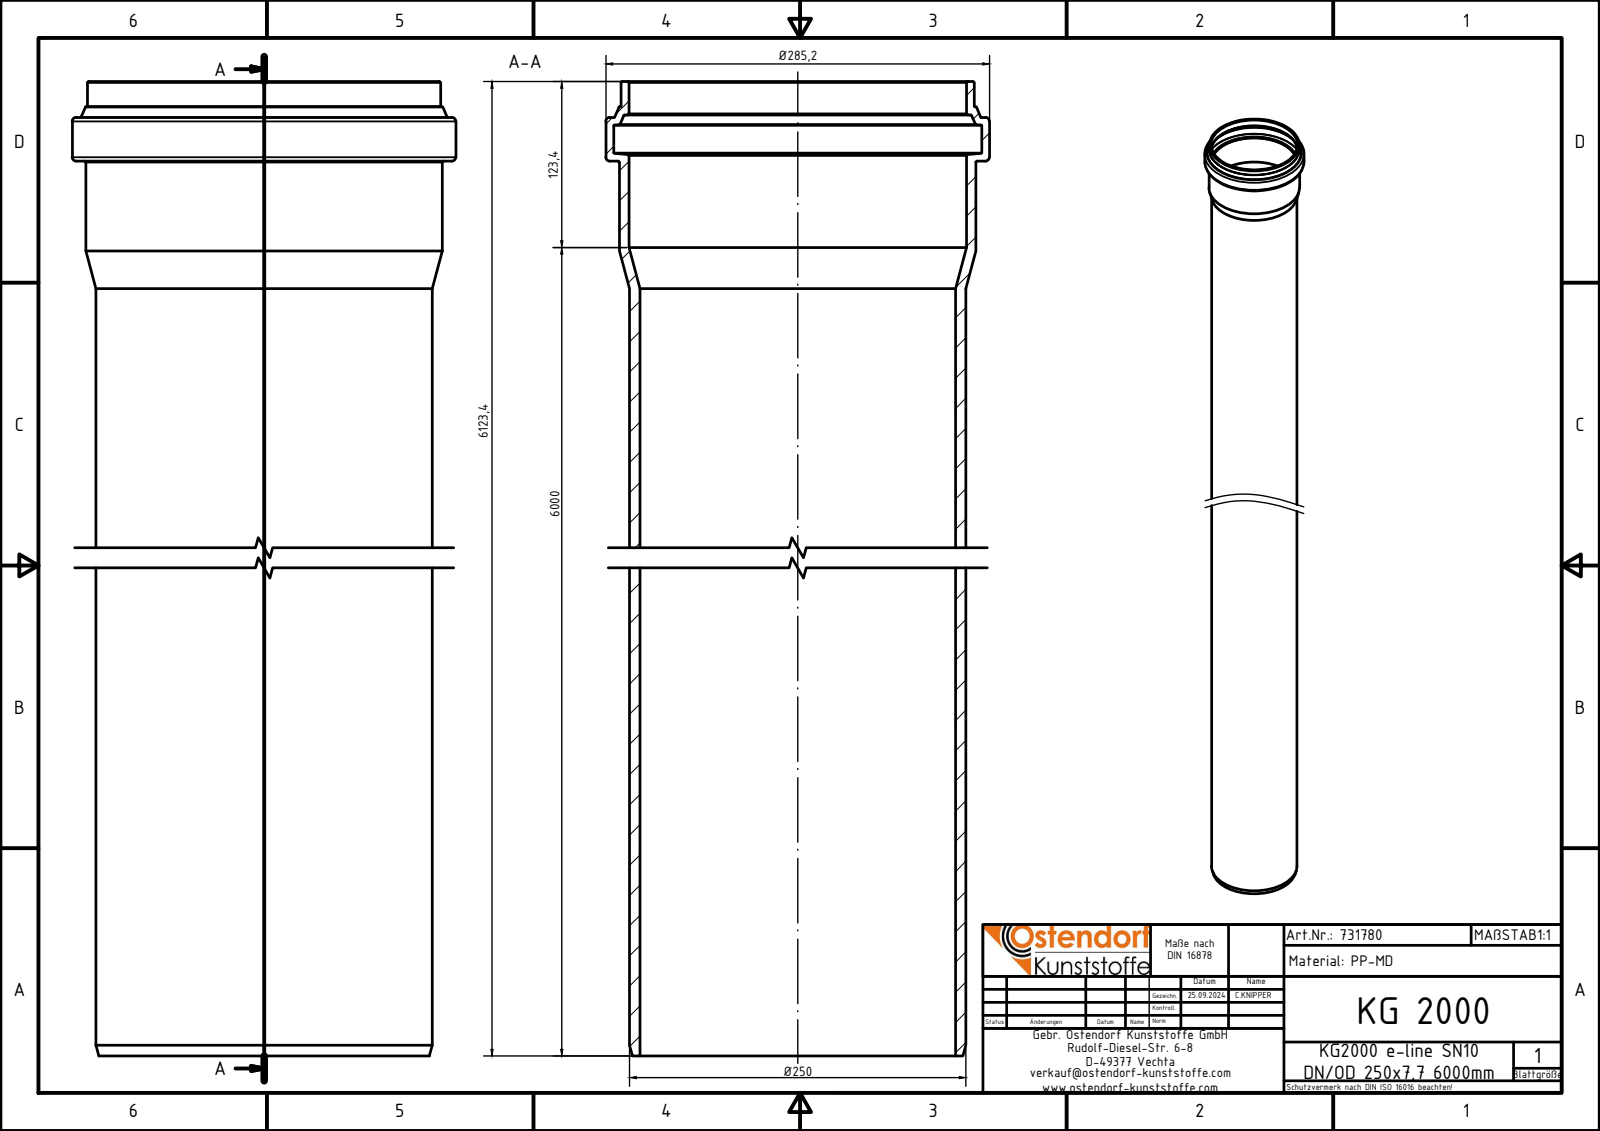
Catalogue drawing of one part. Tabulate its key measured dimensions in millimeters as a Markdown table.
| quantity | value |
| --- | --- |
| part name | 731780z |
| STEP written by | Autodesk Inventor 2024 (AUTOMOTIVE_DESIGN) |
| units | millimeters |
| bodies | 1 solid, 35 faces (5 planar, 8 cylindrical, 22 other) |
| overall size | 6123.4 × 285.2 × 285.2 |
| volume | 35 910 000 mm³ |
| surface area | 9 377 000 mm² |
| round holes (diameter × count) | 234.6 × 1, 251 × 1, 273.6 × 1 |
| round bosses / shafts (diameter × count) | 285.2 × 1, 265 × 1, 262.6 × 1, 250 × 1 |
| main face-to-face distances | 6064.2, 6123.4, 59.2, 6096.7, 32.5, 26.7, 6104.53, 40.33, 7.83, 18.87 |
